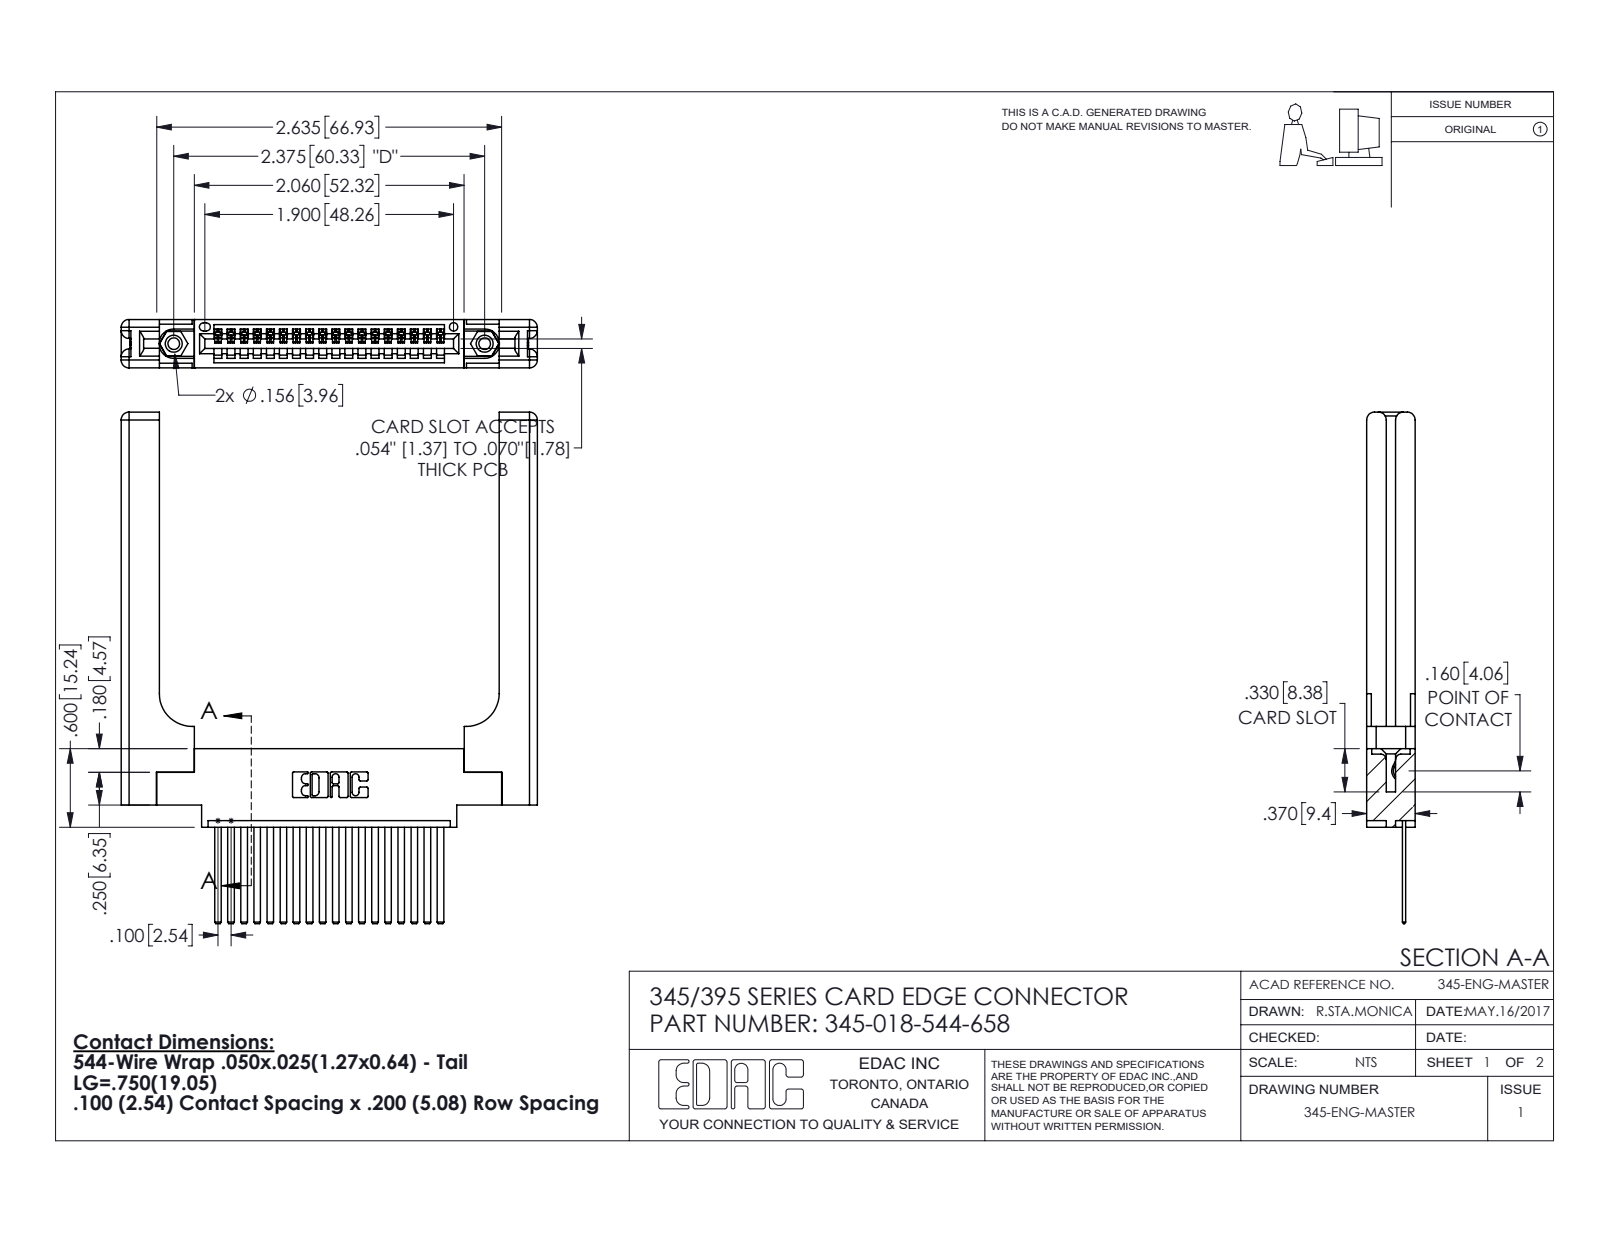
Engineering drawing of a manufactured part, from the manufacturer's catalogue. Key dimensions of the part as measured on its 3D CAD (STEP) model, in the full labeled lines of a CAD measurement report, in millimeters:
Part name (STEP PRODUCT): 345-220-058_345-220-058; 345-018-544-658; 345 Part_0.170 Offset - 0.156 Dia-TH; 345-292-001_345-293-144 (+1 more)
STEP written by: SolidWorks 2016 (CONFIG_CONTROL_DESIGN)
Units: millimetres
Bodies: 23 solids, 1322 faces (880 planar, 382 cylindrical, 60 other)
Overall size (bounding box): 99.2 × 80.7 × 9.4
Volume: 16 100 mm³ · Surface area: 15 790 mm²
Round holes (diameter × count): ⌀2.3 ×2, ⌀3.2 ×2, ⌀4 ×2, ⌀1.6 ×1
Round bosses / shafts (diameter × count): ⌀3.9 ×2
Partial cylindrical surfaces — rounded edges, fillets, slot ends (radius × count): R0.2 ×36, R0.3 ×22, R1.5 ×16, R0.2 ×6, R0.8 ×6, R0.7 ×3, R0.8 ×2, R0.8 ×2
Main face-to-face distances: 9.4, 1.8, 7.6, 2.5, 6.9, 0.6, 3.8, 3.8, 2, 5.6
Hole centre spacings: 6.9, 54.4, 60.3
